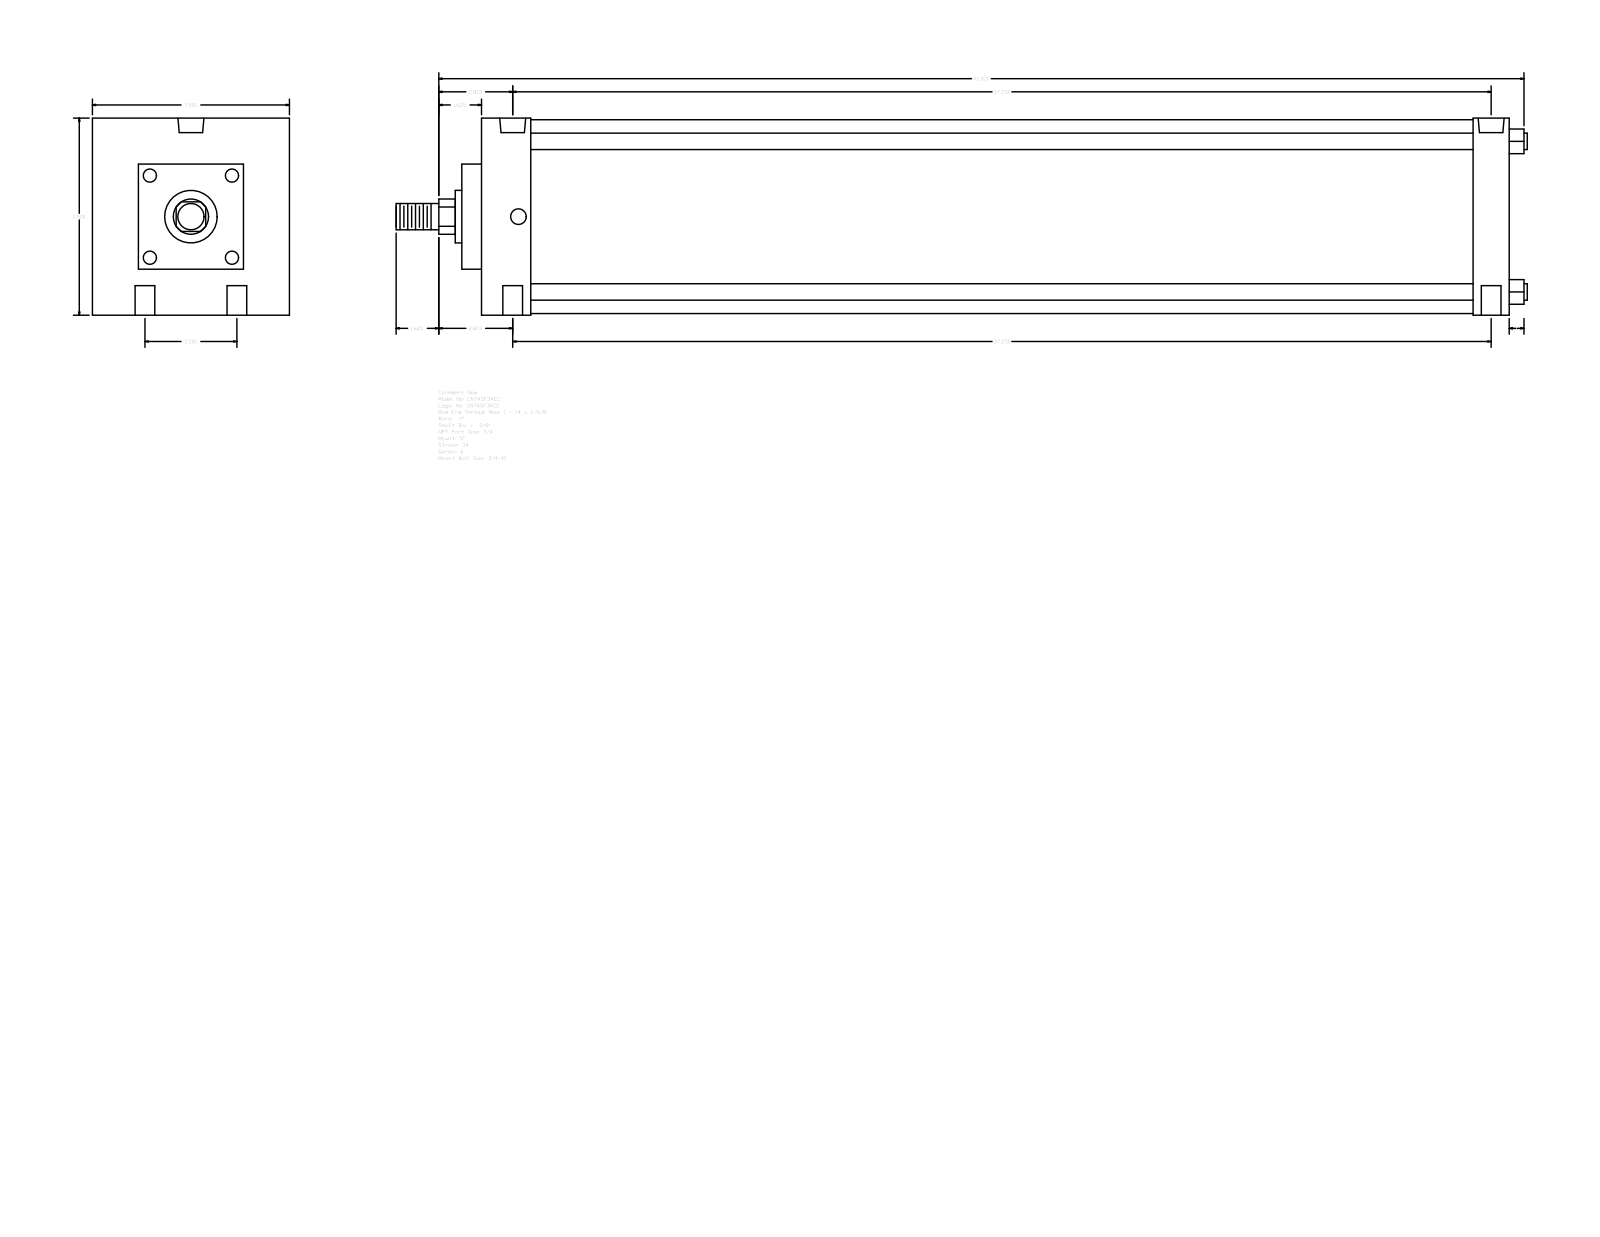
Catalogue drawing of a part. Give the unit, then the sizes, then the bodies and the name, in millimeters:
Units: millimetres
Overall size (bounding box): 1093.79 × 190.5 × 190.5
Round holes (diameter × count): ⌀19.05 ×4, ⌀15.08 ×2, ⌀25.12 ×2
Round bosses / shafts (diameter × count): ⌀15.88 ×4, ⌀187.32 ×1, ⌀50.8 ×1, ⌀34.92 ×1, ⌀25.4 ×1
Partial cylindrical surfaces — rounded edges, fillets, slot ends (radius × count): R17.06 ×1
Main face-to-face distances: 190.5, 993.78, 19.04, 1012.82, 66.67, 977.89, 47.63, 958.85, 911.22, 946.15
Hole centre spacings: 44.45, 947.19, 946.15, 88.9, 950.32, 935.03
Bodies: 0 solids, 93 faces (67 planar, 26 cylindrical, 0 other)
Part name (STEP PRODUCT): A_SF__0700_1.375
STEP written by: GSSL Pune (CONFIG_CONTROL_DESIGN)
